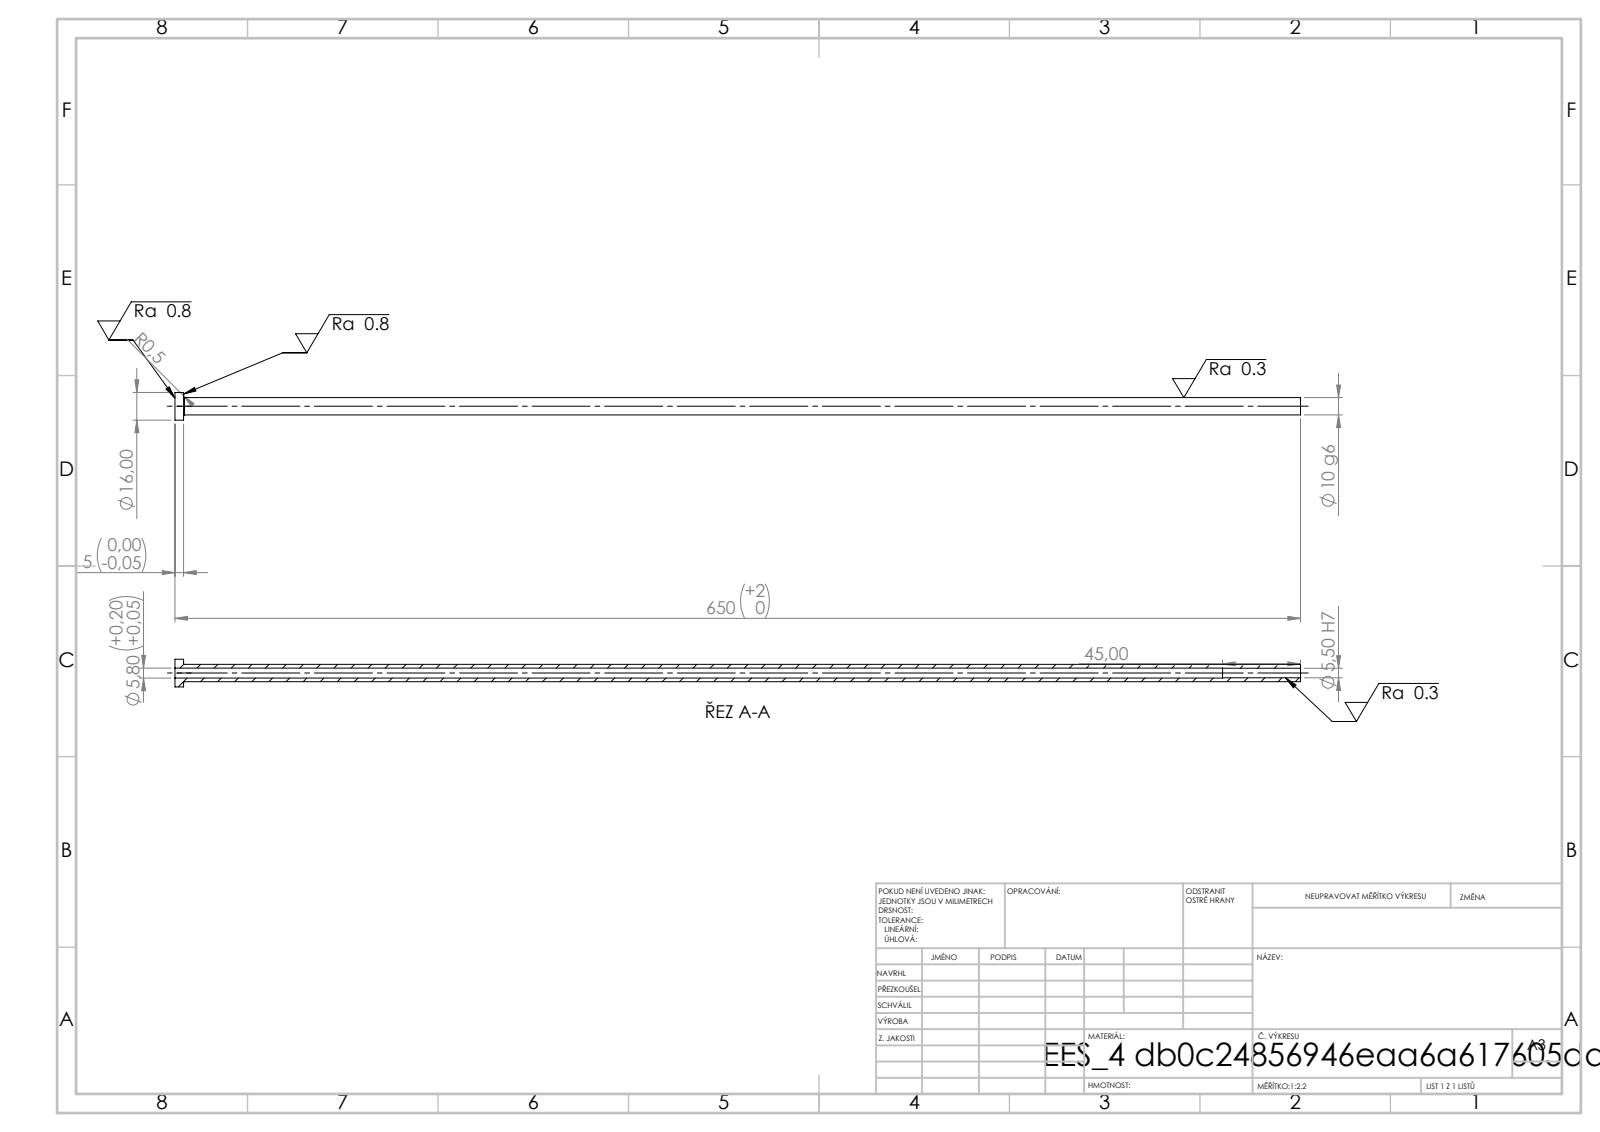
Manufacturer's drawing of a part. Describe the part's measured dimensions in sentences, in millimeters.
Its 3-D file was written by "SolidWorks 2019 (CONFIG_CONTROL_DESIGN)". It is 1 solid with 14 faces: 4 planar, 8 cylindrical and 2 other. Overall it measures 650 by 16 by 16 millimeters. Its volume is 34 612 cubic millimeters and its surface area 32 664 square millimeters. Round holes: 1 of diameter 5.5, 1 of diameter 5.8. Round bosses or shafts: 1 of diameter 16, 1 of diameter 10. The main face-to-face distances are 5, 650, 645, 605, 600, 45.
